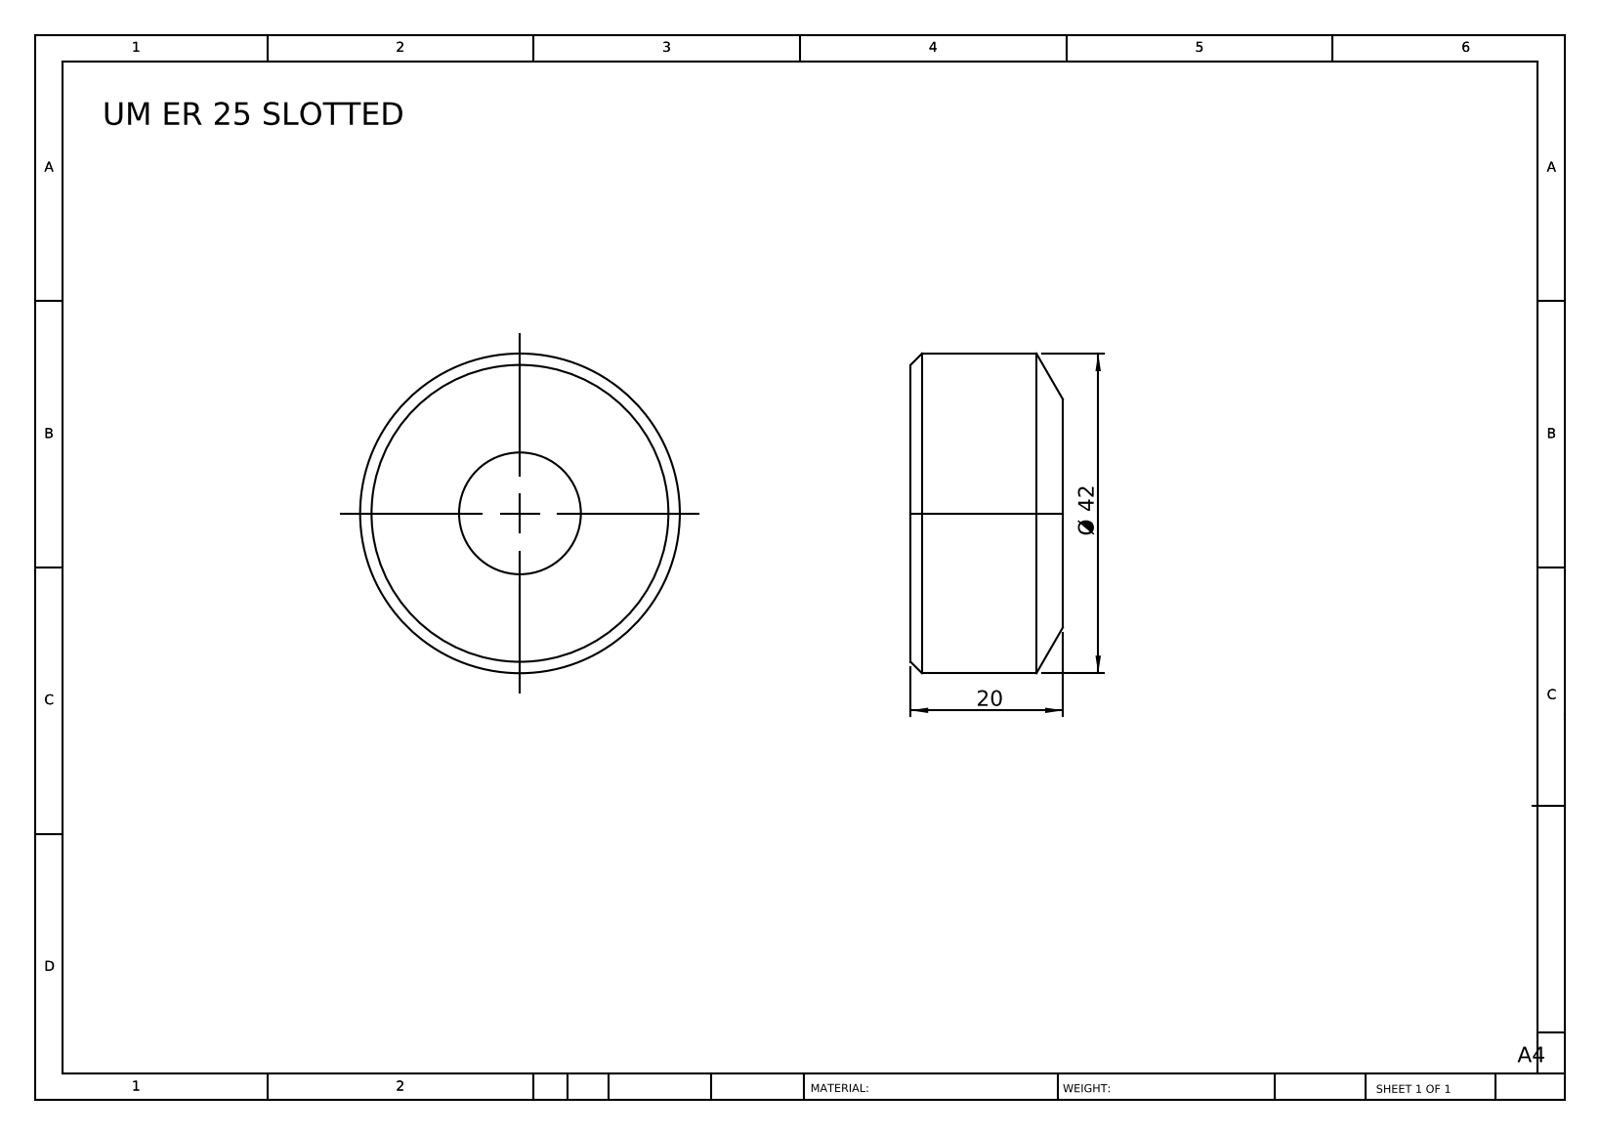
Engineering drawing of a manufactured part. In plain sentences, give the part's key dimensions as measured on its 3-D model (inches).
The part is named "UM ER 25 SLOTTED". Its 3-D file was written by "SolidWorks 2014 (CONFIG_CONTROL_DESIGN)". It is 1 solid with 10 faces: 2 planar, 4 cylindrical and 4 other. Overall it measures 1.654 by 1.654 by 0.787 inches. Its volume is 1.361 cubic inches and its surface area 8.59 square inches. Round holes: 1 of diameter 0.63. Round bosses or shafts: 1 of diameter 1.654. The main face-to-face distances are 0.787.
